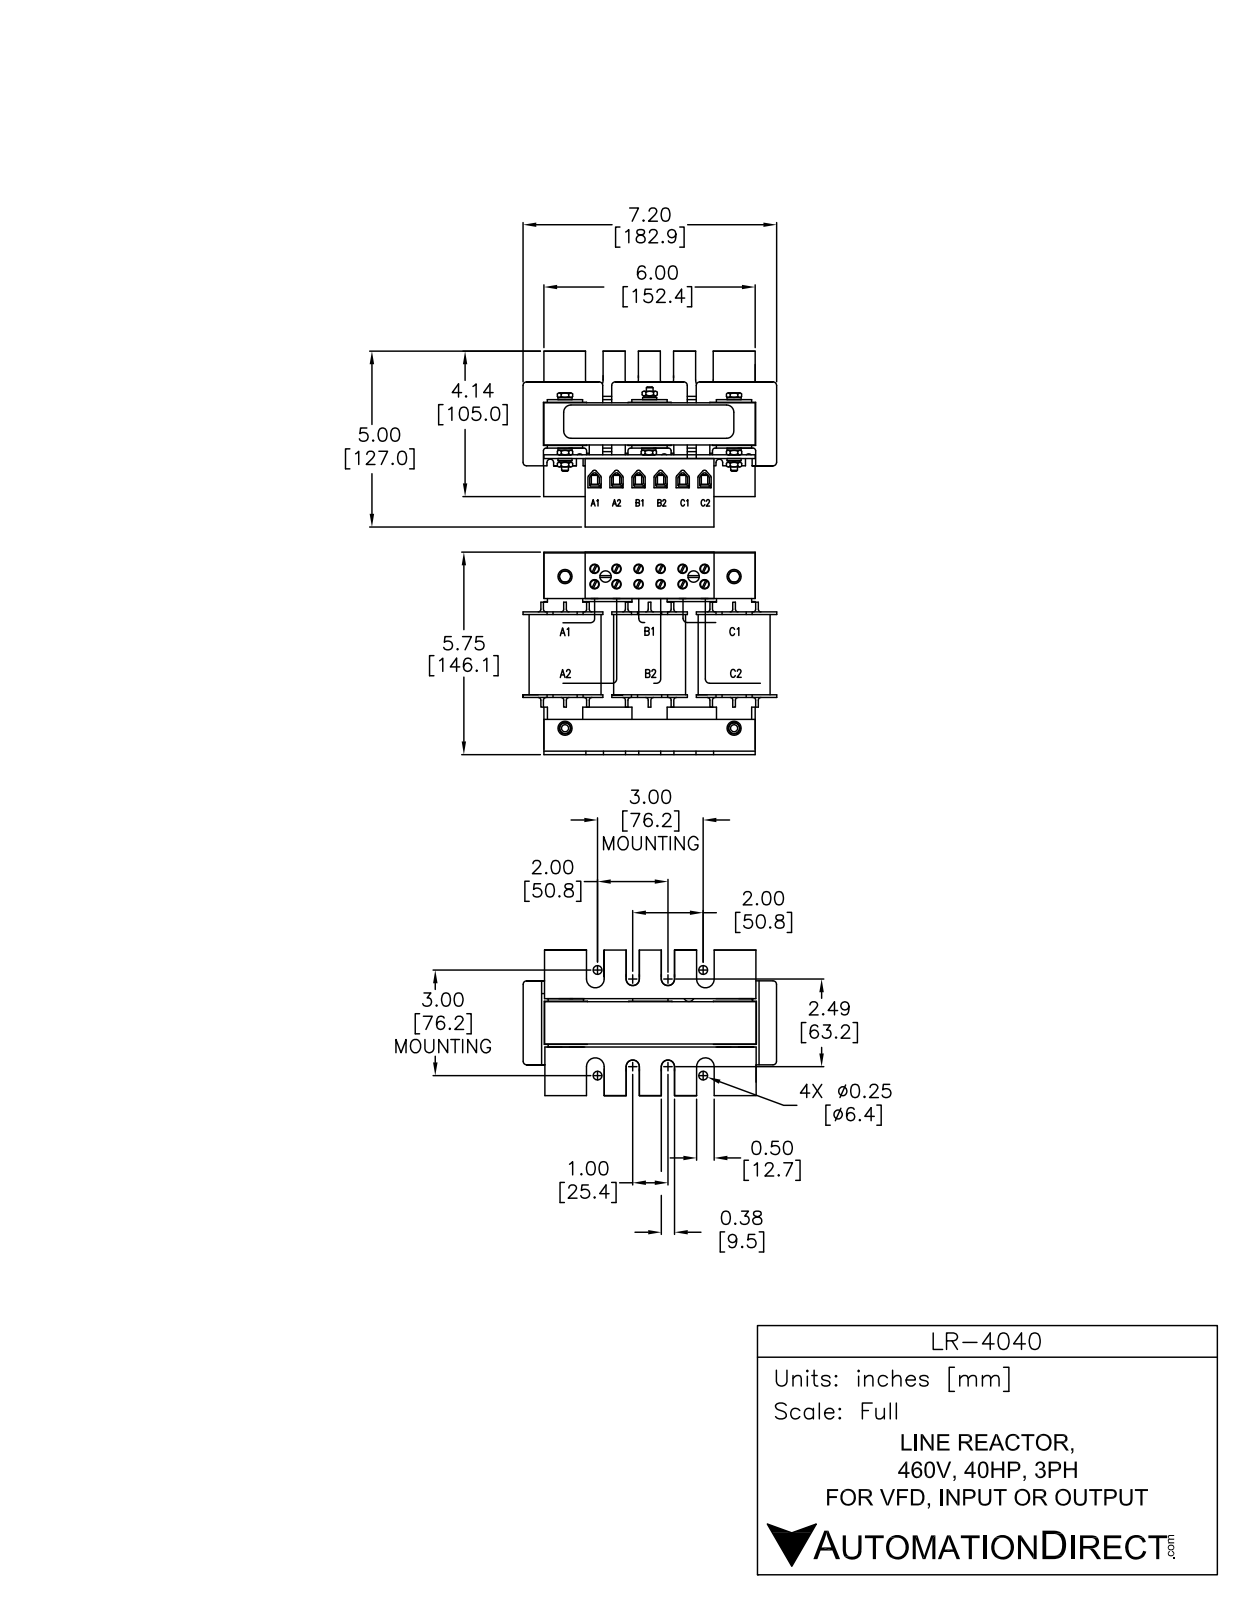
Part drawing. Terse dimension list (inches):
name: LR-4040
written by: SolidWorks 2011 (AUTOMOTIVE_DESIGN)
unit: in
bodies: 14 solids, 819 faces (597 planar, 214 cylindrical, 8 other)
size: 7.018 × 5.701 × 4.35
volume: 68.65 in³; area: 310.2 in²
holes: 12× ⌀0.276, 5× ⌀0.305
bosses: 5× ⌀0.472, 5× ⌀0.413, 2× ⌀0.183, 1× ⌀0.184, 1× ⌀0.183, 1× ⌀0.183
rounds: 24× R0.106, 12× R0.197, 12× R0.276, 6× R0.089, 4× R0.059, 4× R0.192, 4× R0.251, 2× R0.128
face distances: 0.079, 2.441, 0.482, 1.86, 1.781, 0.187, 1.299, 0.108, 2.362, 0.561
hole spacings: 0.63, 1.26, 0.376, 0.394, 0.77, 0.96, 0.981, 1.335
